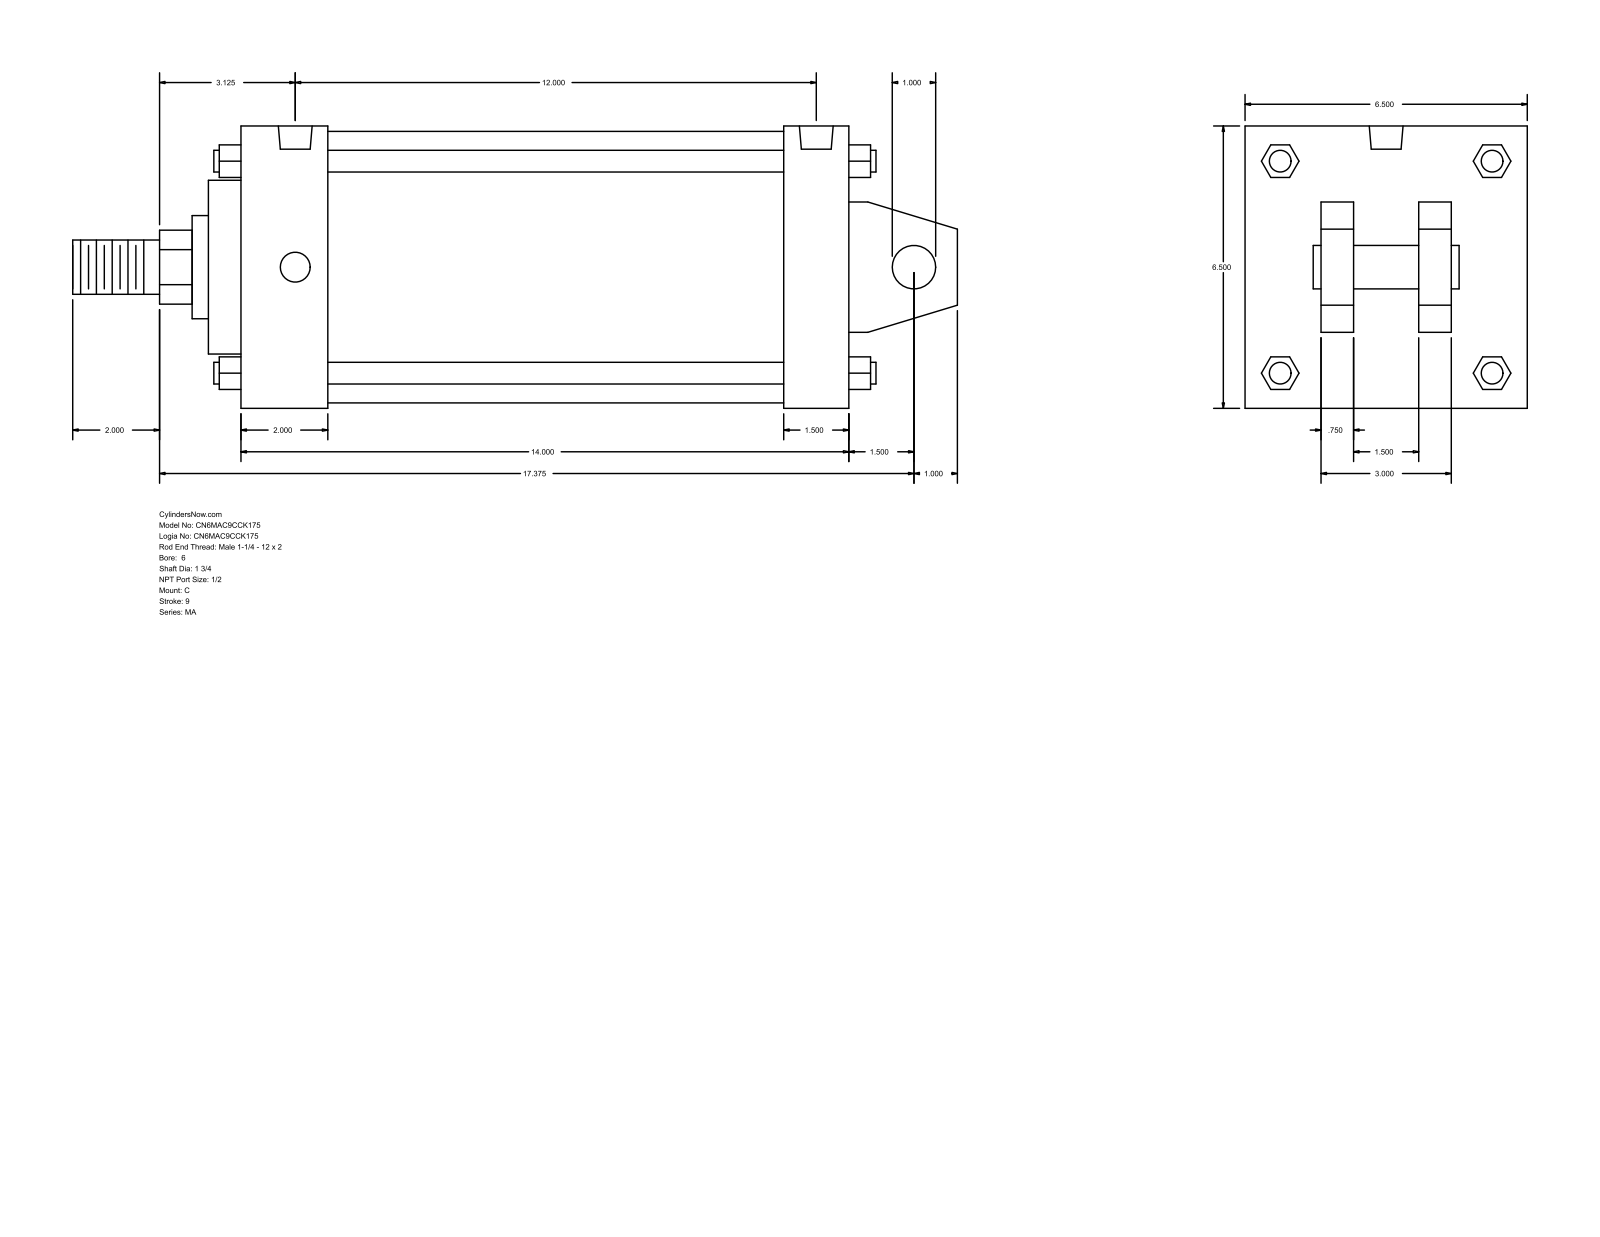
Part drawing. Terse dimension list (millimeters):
name: MA_C__0600_1.75
written by: GSSL Pune (CONFIG_CONTROL_DESIGN)
unit: mm
bodies: 0 solids, 141 faces (109 planar, 32 cylindrical, 0 other)
size: 517.52 × 165.1 × 165.1
holes: 4× ⌀17.46, 2× ⌀19.77
bosses: 4× ⌀12.7, 1× ⌀158.75, 1× ⌀101.6, 1× ⌀60.33, 1× ⌀44.45, 1× ⌀31.75, 1× ⌀25.4
rounds: 1× R21.63
face distances: 165.1, 355.61, 19.05, 63.5, 101.6, 50.8, 44.45, 120.65, 57.15, 304.81
hole spacings: 304.8
